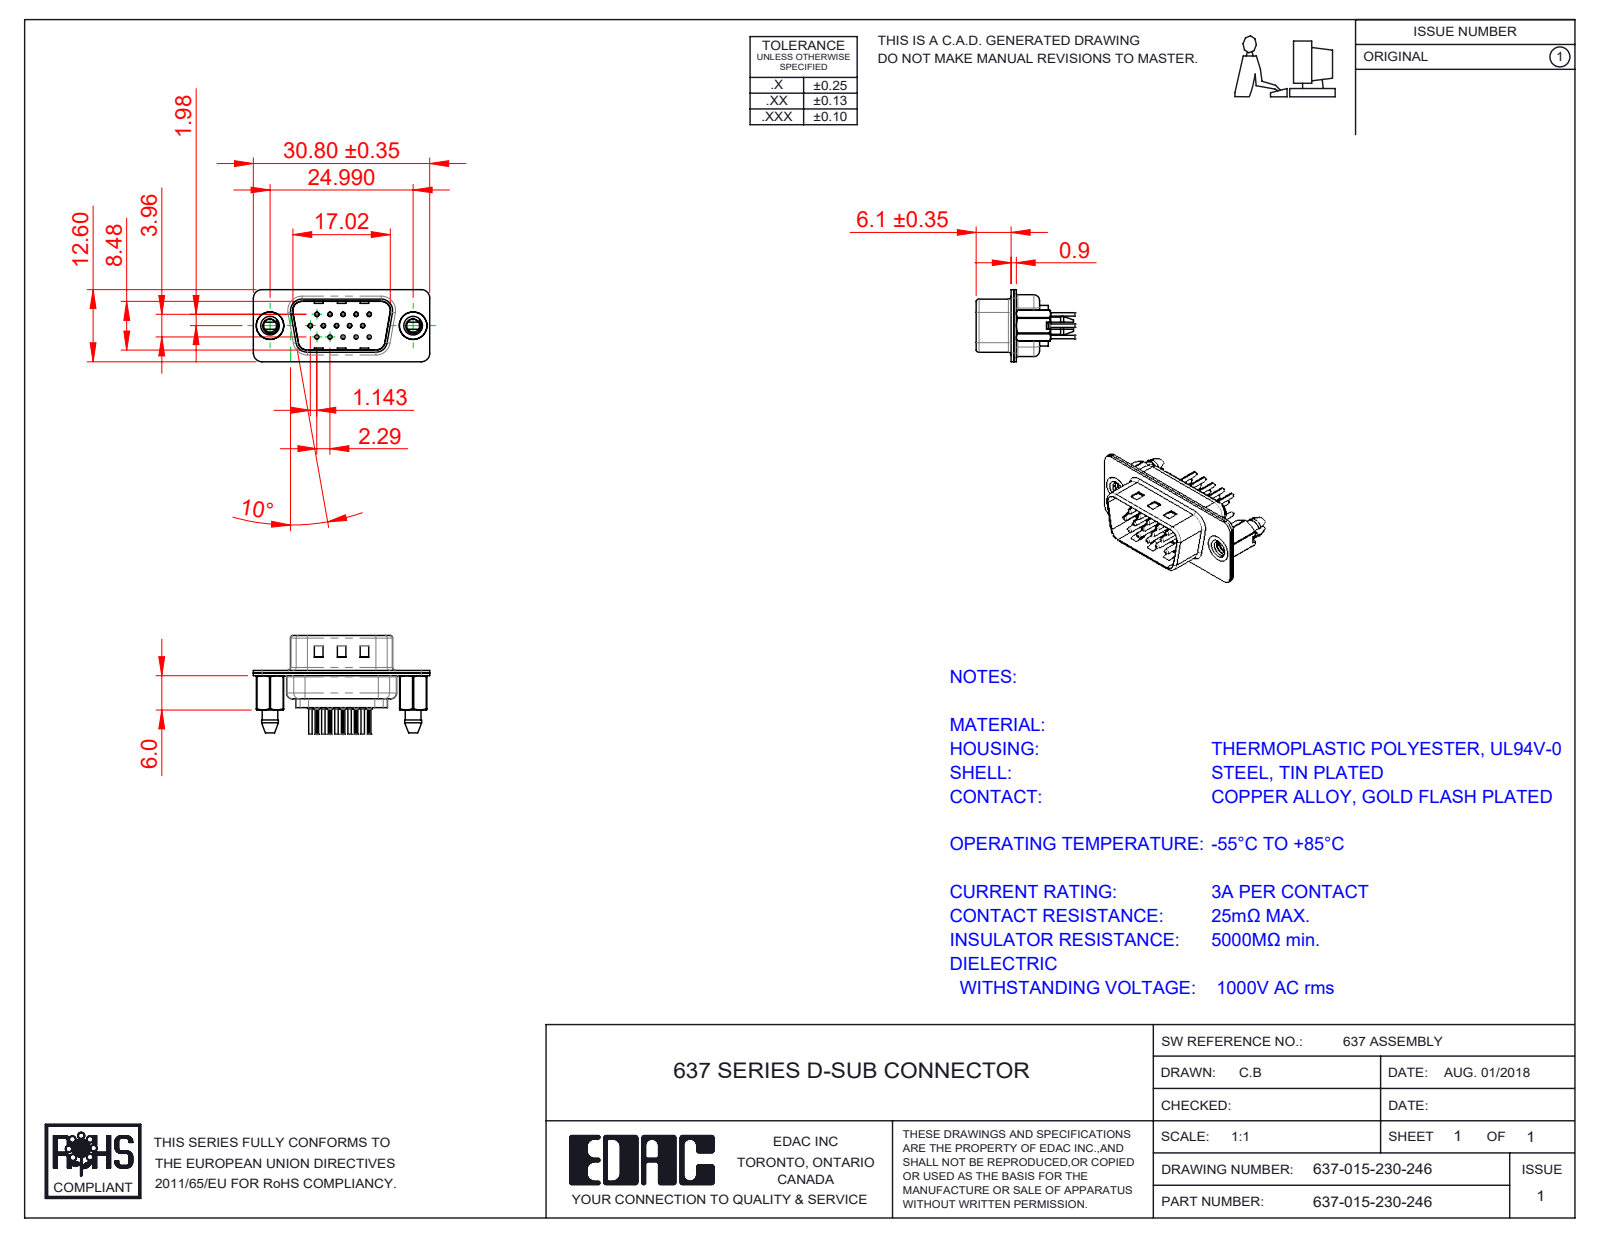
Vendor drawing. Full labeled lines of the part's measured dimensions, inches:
Part name (STEP PRODUCT): 637 4-40 Threaded Boardlock_LP; 637 Housing_15 Contacts; 637 Contact Row 2_30; 637 Shell Rear_15 Contacts (+4 more)
STEP written by: SolidWorks 2020 (CONFIG_CONTROL_DESIGN)
Units: inches
Bodies: 20 solids, 1878 faces (499 planar, 716 cylindrical, 663 other)
Overall size (bounding box): 1.213 × 0.679 × 0.496
Volume: 0.087 in³ · Surface area: 7.646 in²
Round holes (diameter × count): ⌀0.008 ×15, ⌀0.014 ×15, ⌀0.043 ×15, ⌀0.063 ×15, ⌀0.089 ×2, ⌀0.157 ×2, ⌀0.189 ×2
Round bosses / shafts (diameter × count): ⌀0.079 ×15, ⌀0.059 ×15, ⌀0.03 ×15, ⌀0.024 ×15, ⌀0.193 ×2
Partial cylindrical surfaces — rounded edges, fillets, slot ends (radius × count): R0.004 ×30, R0.059 ×18, R0.079 ×12, R0.02 ×8, R0.063 ×6, R0.01 ×4, R0.022 ×4, R0.028 ×4
Main face-to-face distances: 0.018, 0.016, 0.035, 0.028, 0.35, 0.334, 0.041, 0.256, 0.179, 0.012
Hole centre spacings: 0.156, 0.09, 0.18, 0.09, 0.238, 0.27, 0.312, 0.238
